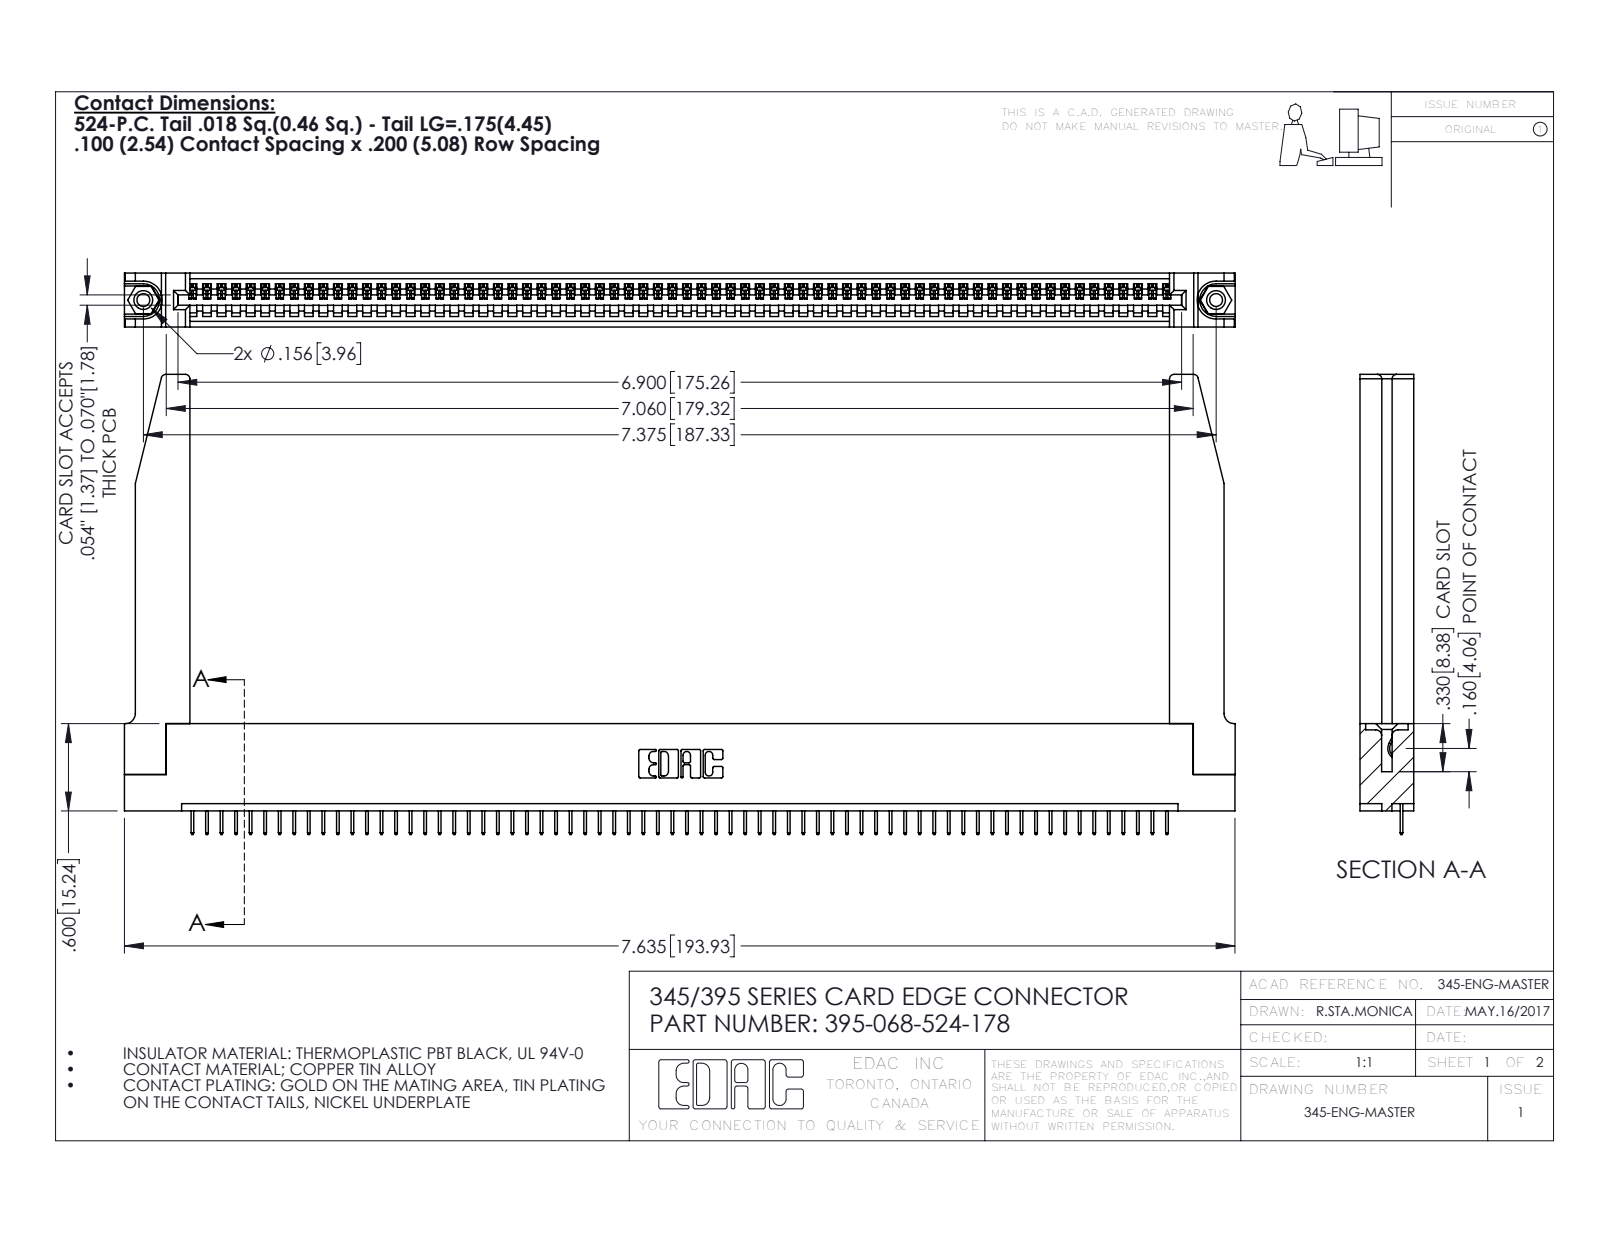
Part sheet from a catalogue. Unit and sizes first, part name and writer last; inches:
Units: inches
Overall size (bounding box): 7.636 × 3.162 × 0.37
Round holes (diameter × count): ⌀0.089 ×2, ⌀0.125 ×2, ⌀0.156 ×2, ⌀0.064 ×1
Round bosses / shafts (diameter × count): ⌀0.155 ×2
Partial cylindrical surfaces — rounded edges, fillets, slot ends (radius × count): R0.006 ×136, R0.01 ×22, R0.03 ×8, R0.007 ×6, R0.031 ×6, R0.026 ×3, R0.031 ×2, R0.04 ×2
Main face-to-face distances: 0.37, 0.072, 0.298, 0.2, 0.098, 0.272, 0.025, 0.225, 0.072, 0.149
Hole centre spacings: 0.27, 7.139, 7.375
Volume: 1.595 in³ · Surface area: 47.66 in²
Bodies: 73 solids, 4576 faces (3350 planar, 1174 cylindrical, 52 other)
Part name (STEP PRODUCT): 345-292-001_345-293-124; 395-068-524-178; 345-250-001_345-250-001-102; 345 Part_Flush Mounting Lugs - 0.156 Dia-TH (+1 more)
STEP written by: SolidWorks 2016 (CONFIG_CONTROL_DESIGN)
